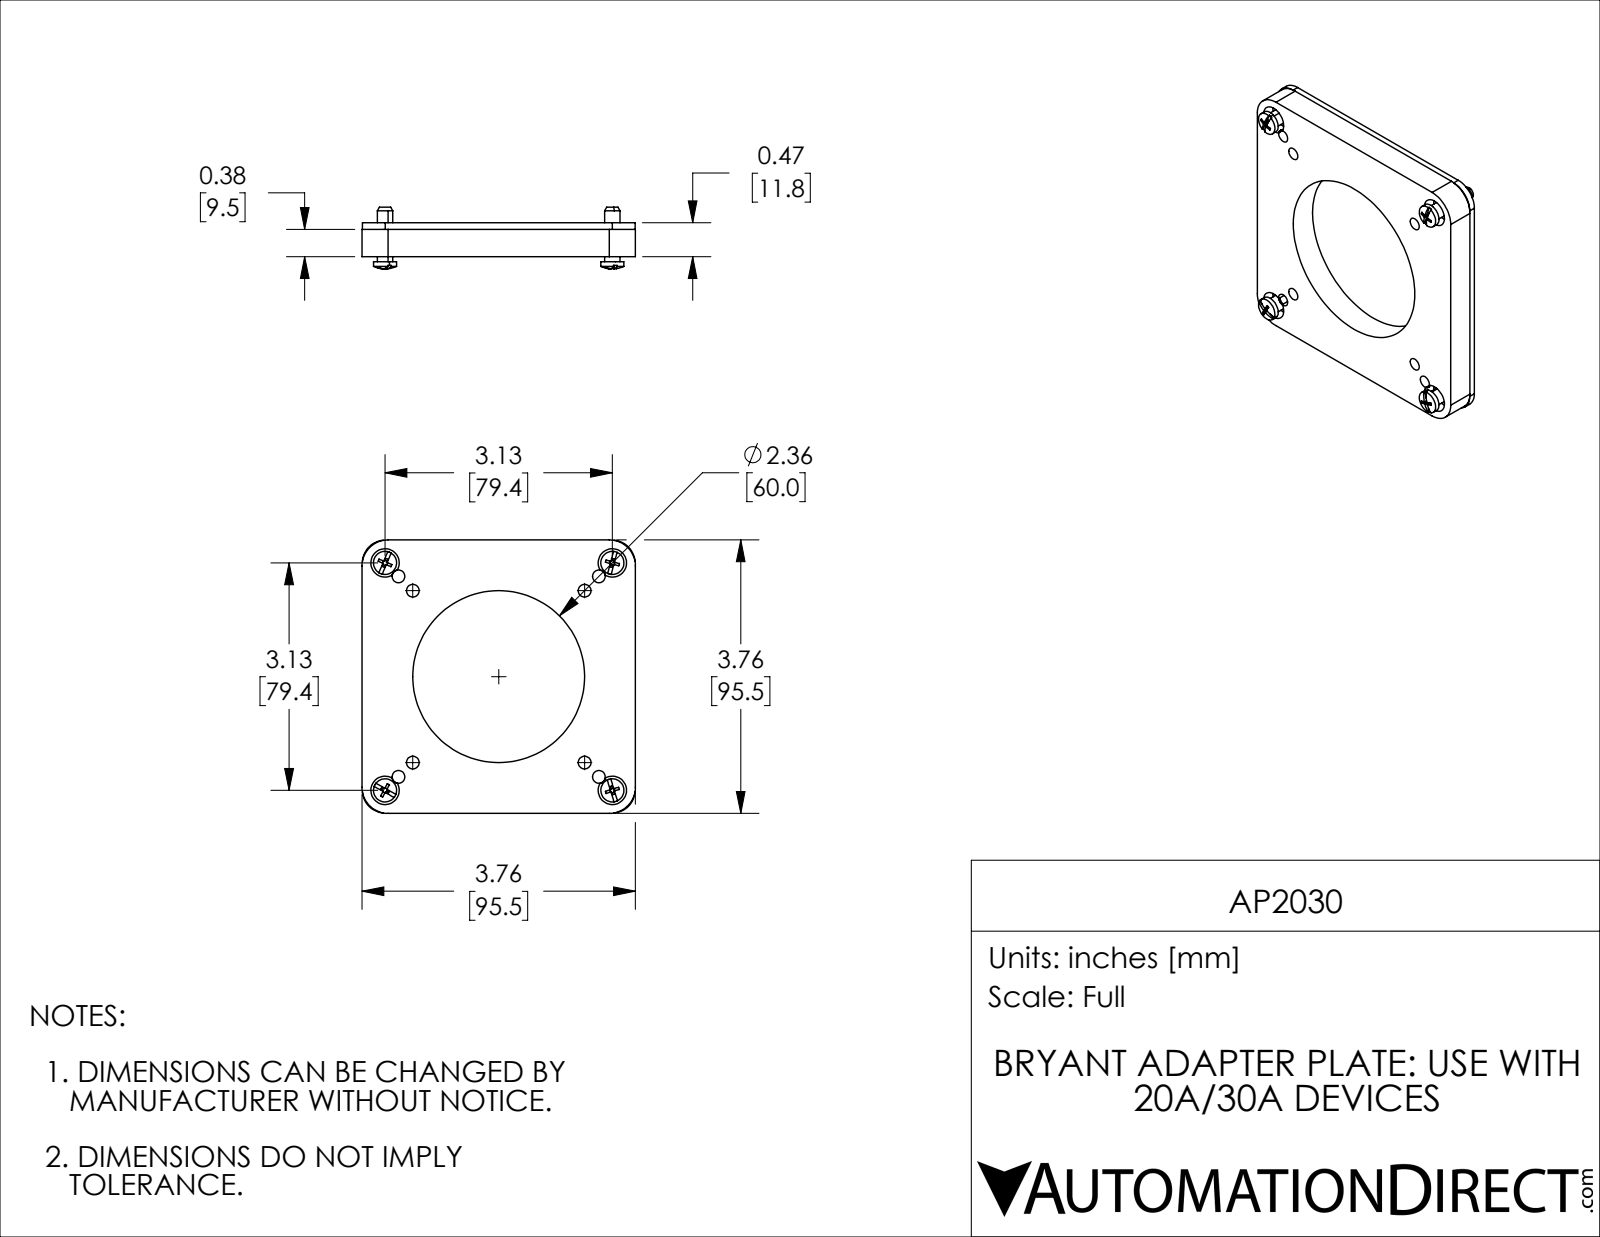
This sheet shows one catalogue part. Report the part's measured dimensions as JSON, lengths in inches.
{"part_name": "AP2030", "step_written_by": "SolidWorks 2021 (CONFIG_CONTROL_DESIGN)", "units": "inches", "bodies": {"solids": 6, "faces": 204, "planar": 108, "cylindrical": 80, "other": 16}, "overall_size": [3.76, 3.76, 0.847], "volume_in3": 4.223, "surface_area_in2": 50.21, "round_holes": [[0.216, 8], [0.175, 4], [0.175, 4], [0.219, 4], [0.39, 4], [2.362, 1], [2.834, 1]], "round_bosses_or_shafts": [[0.318, 4], [0.212, 4]], "partial_cylinders_radius": [[0.089, 4], [0.314, 4], [0.36, 4]], "face_to_face_distances": [0.375, 0.09, 0.465, 3.76, 3.76, 3.755, 3.75, 0.285, 0.195, 0.18], "hole_center_spacings": [2.77, 2.947, 0.262, 0.539, 1.949, 2.21, 2.362, 2.566]}
